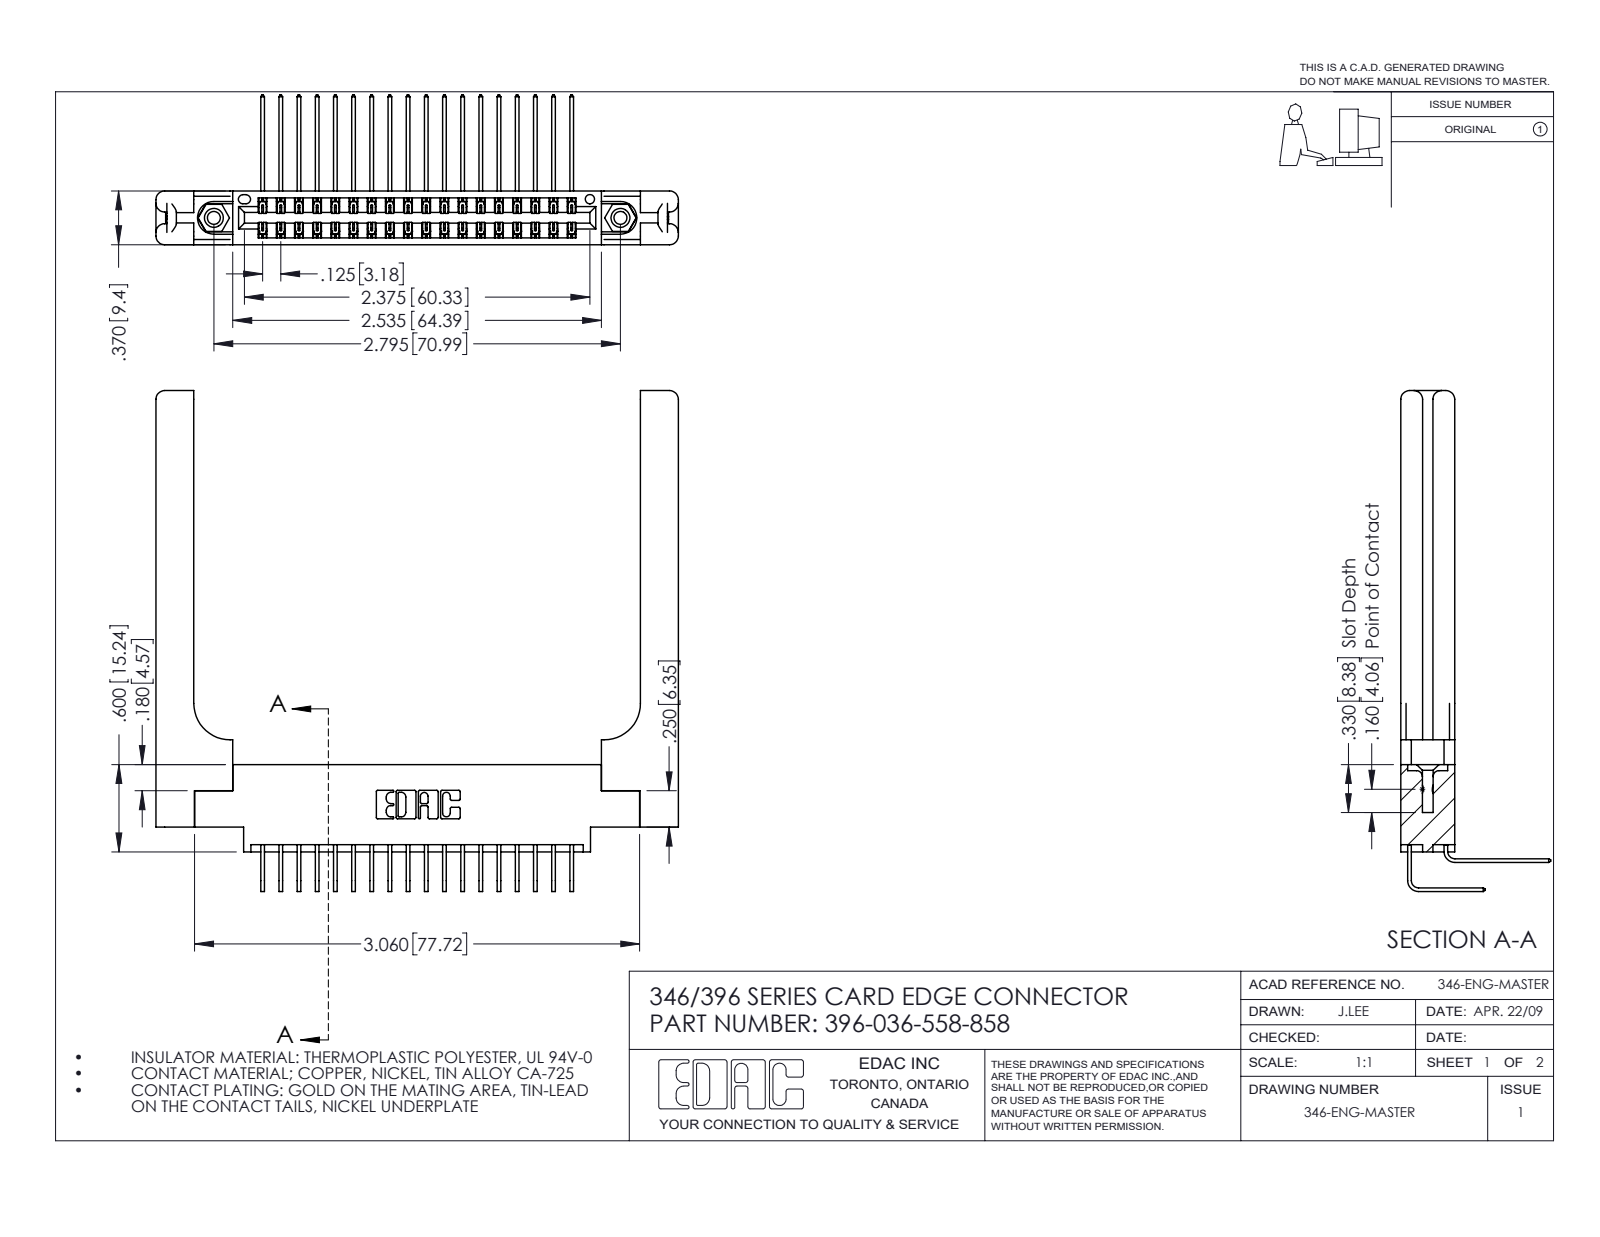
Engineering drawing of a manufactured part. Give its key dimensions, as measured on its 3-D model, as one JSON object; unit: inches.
{"part_name": "345-292-001_558 559 Tail - 1; 346 Part_0.170 Offset - 0.156 Dia-TH; 346-220-058_345-220-058; 396-036-558-858 (+2 more)", "step_written_by": "SolidWorks 2016 (CONFIG_CONTROL_DESIGN)", "units": "inches", "bodies": {"solids": 41, "faces": 2326, "planar": 1560, "cylindrical": 706, "other": 60}, "overall_size": [3.591, 3.443, 1.03], "volume_in3": 0.992, "surface_area_in2": 27.61, "round_holes": [[0.089, 2], [0.125, 2], [0.156, 2], [0.064, 1]], "round_bosses_or_shafts": [[0.155, 2]], "partial_cylinders_radius": [[0.006, 54], [0.01, 22], [0.06, 16], [0.007, 6], [0.031, 6], [0.026, 3], [0.014, 2], [0.022, 2]], "face_to_face_distances": [0.37, 0.072, 0.322, 0.048, 0.15, 0.148, 0.025, 0.25, 0.298, 0.077], "hole_center_spacings": [0.246, 2.588, 2.795]}
